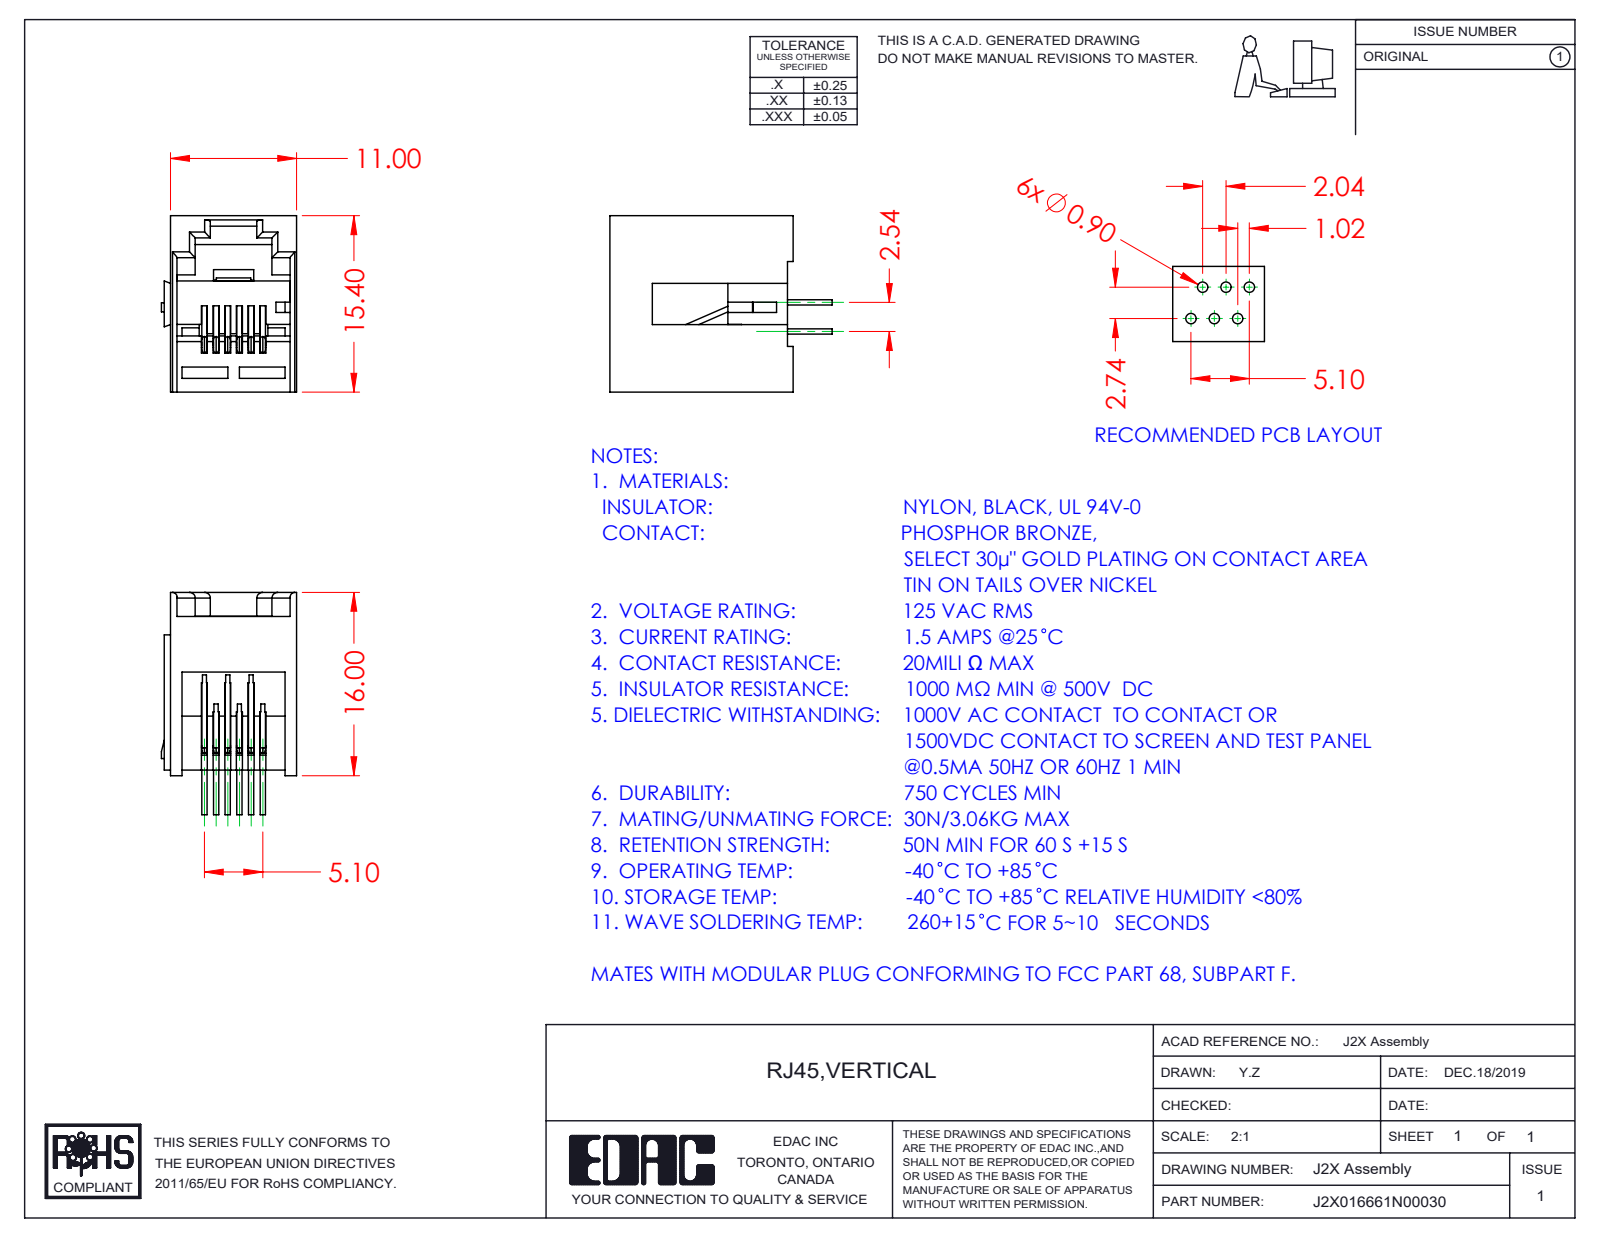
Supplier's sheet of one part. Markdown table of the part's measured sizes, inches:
| quantity | value |
| --- | --- |
| part name | 2X Insulator; J2X016661N00030; 2X Contacts; 2X Contact Lock |
| STEP written by | SolidWorks 2016 (CONFIG_CONTROL_DESIGN) |
| units | inches |
| bodies | 8 solids, 466 faces (333 planar, 97 cylindrical, 36 other) |
| overall size | 0.764 × 0.606 × 0.465 |
| volume | 0.074 in³ |
| surface area | 4.408 in² |
| round bosses / shafts (diameter × count) | 0.018 × 24 |
| partial cylindrical surfaces (radius × count) | 0.02 × 7, 0.006 × 2, 0.012 × 2, 0.016 × 2, 0.008 × 1 |
| main face-to-face distances | 0.039, 0.433, 0.08, 0.04, 0.02, 0.022, 0.02, 0.394, 0.472, 0.411 |
